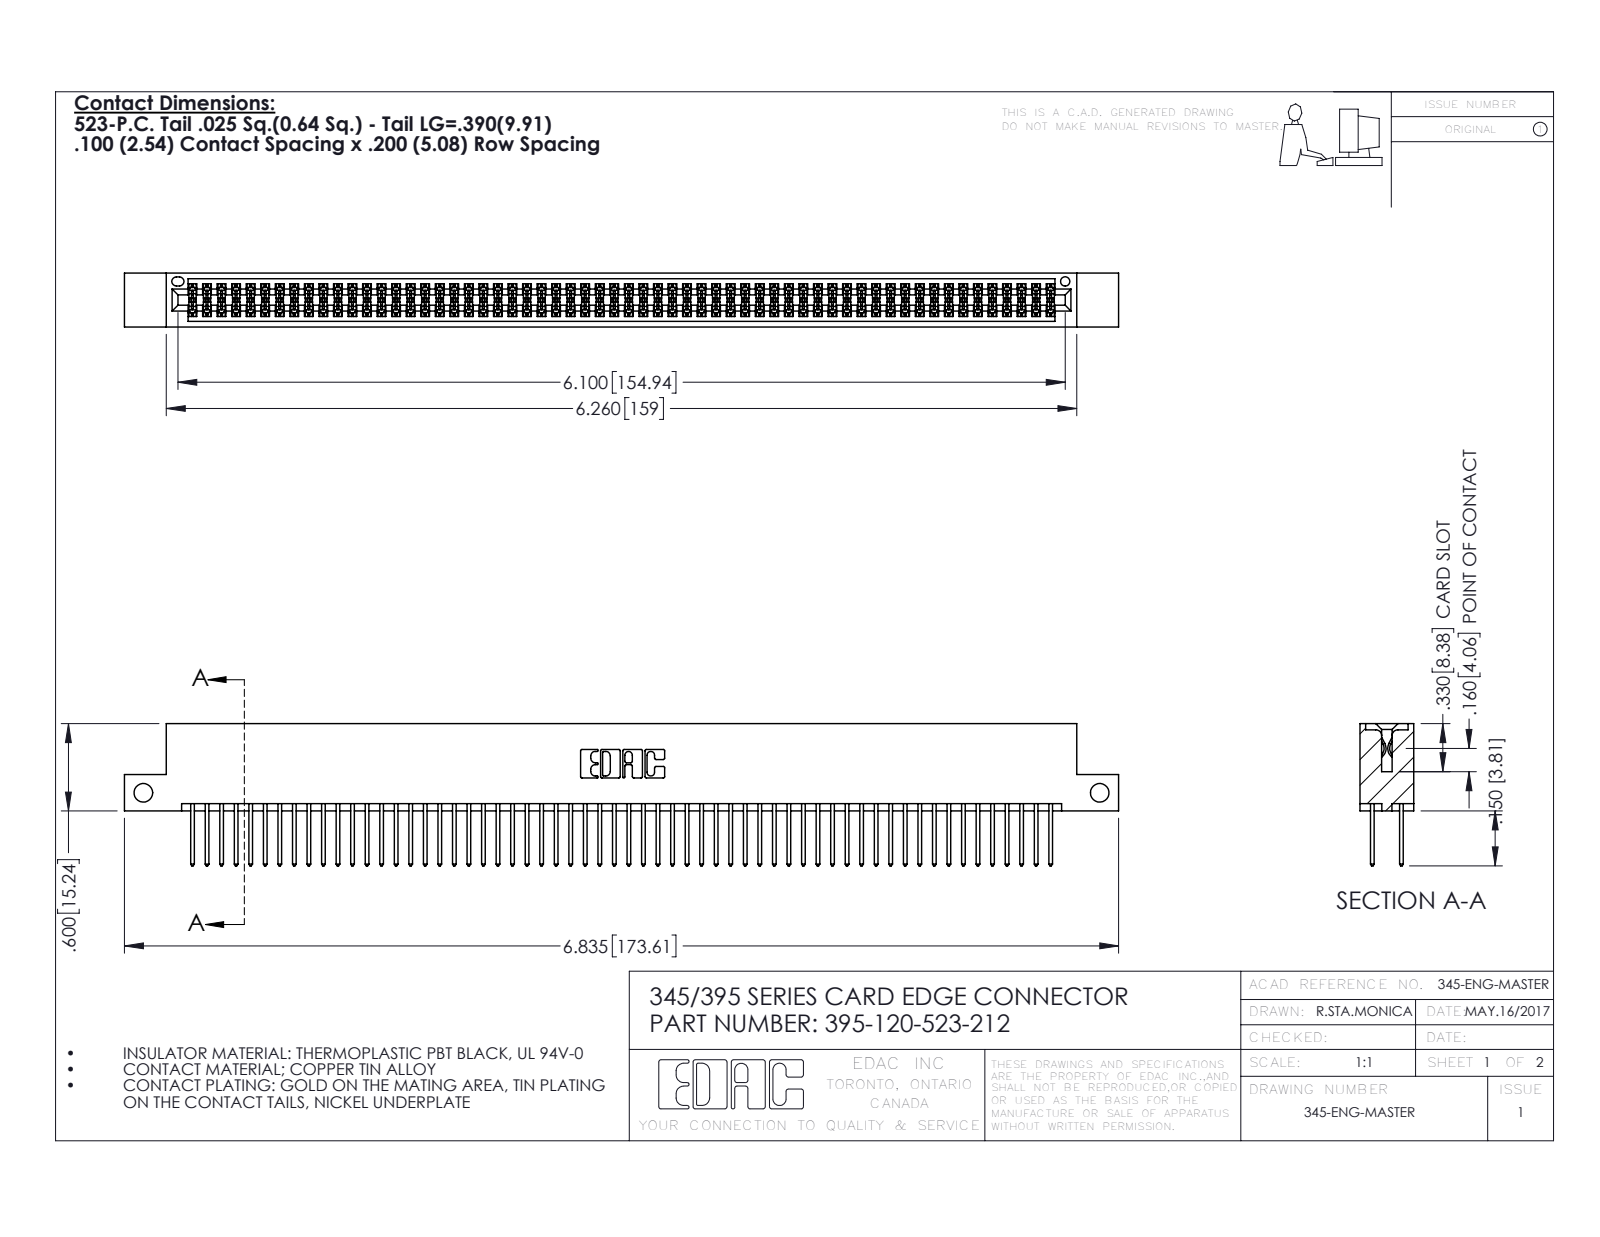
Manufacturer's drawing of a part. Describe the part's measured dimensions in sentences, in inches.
The part is named "345 Part_Flush Mounting Lugs - Side Mount; 395-120-523-212; 345-292-001_345-293-123". Its 3-D file was written by "SolidWorks 2016 (CONFIG_CONTROL_DESIGN)". It is 121 solids with 6126 faces: 4040 planar, 2086 cylindrical and 0 other. Overall it measures 6.835 by 0.977 by 0.37 inches. Its volume is 1.049 cubic inches and its surface area 41.43 square inches. Round holes: 2 of diameter 0.128, 1 of diameter 0.064. Partial cylindrical surfaces (rounded edges, fillets, slot ends): 180 of radius 0.006, 120 of radius 0.01, 22 of radius 0.01, 6 of radius 0.007, 6 of radius 0.031, 3 of radius 0.026, 2 of radius 0.014, 2 of radius 0.019. The main face-to-face distances are 0.298, 0.072, 0.2, 0.098, 0.272, 0.025, 0.37, 0.225, 0.175, 0.149. The hole center spacings are 6.575.
